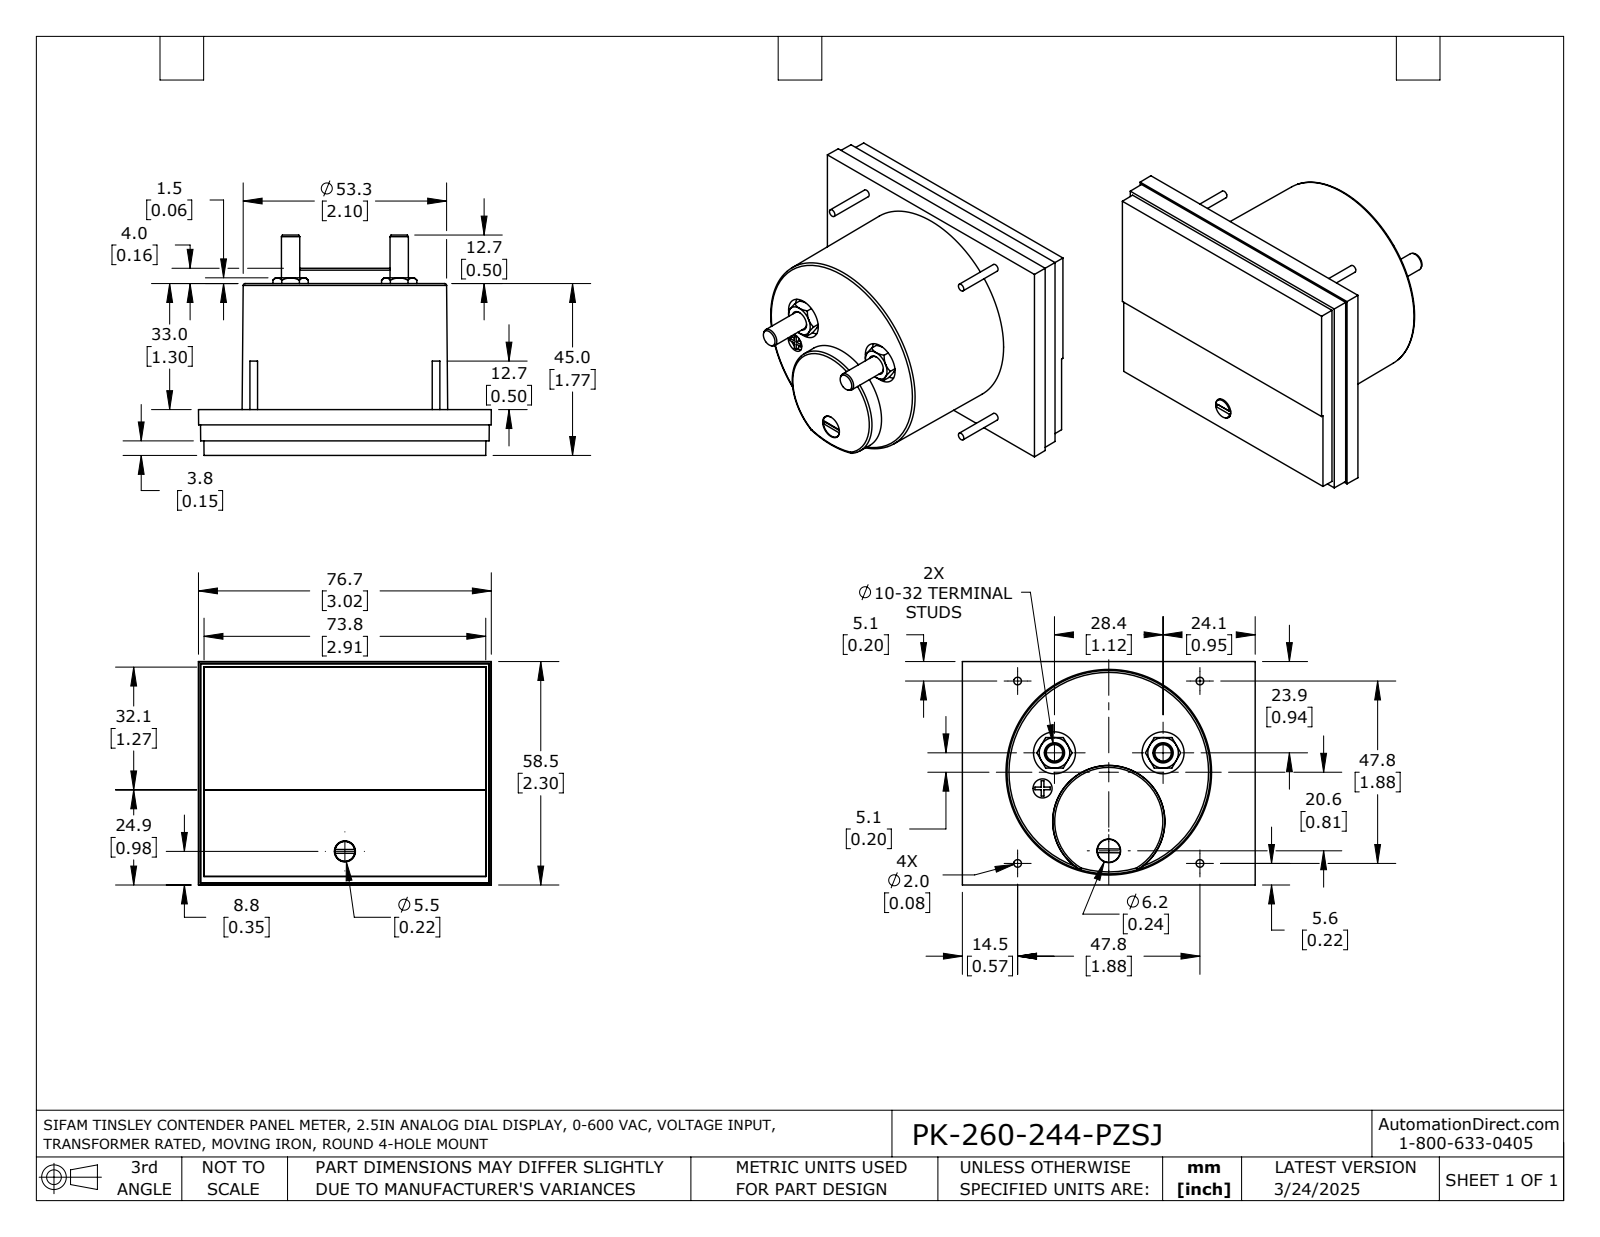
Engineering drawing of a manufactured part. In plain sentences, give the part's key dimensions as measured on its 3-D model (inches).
The part is named "PK-260-244-PZSJ". Its 3-D file was written by "SolidWorks 2021 (AUTOMOTIVE_DESIGN)". It is 1 solid with 192 faces: 95 planar, 37 cylindrical and 60 other. Overall it measures 3.02 by 2.303 by 2.272 inches. Its volume is 7.657 cubic inches and its surface area 36.55 square inches. Round holes: 3 of diameter 0.197, 2 of diameter 0.433, 1 of diameter 0.209, 1 of diameter 0.217, 1 of diameter 0.244. Round bosses or shafts: 4 of diameter 0.079, 2 of diameter 0.189, 1 of diameter 0.236, 1 of diameter 0.205. Partial cylindrical surfaces (rounded edges, fillets, slot ends): 1 of radius 0.033. The main face-to-face distances are 0.02, 0.472, 0.13, 0.322, 0.15, 0.453, 0.057, 0.077, 0.396, 0.073. The hole center spacings are 1.155, 1.16, 0.387, 0.938, 0.942, 1.12, 1.295.
